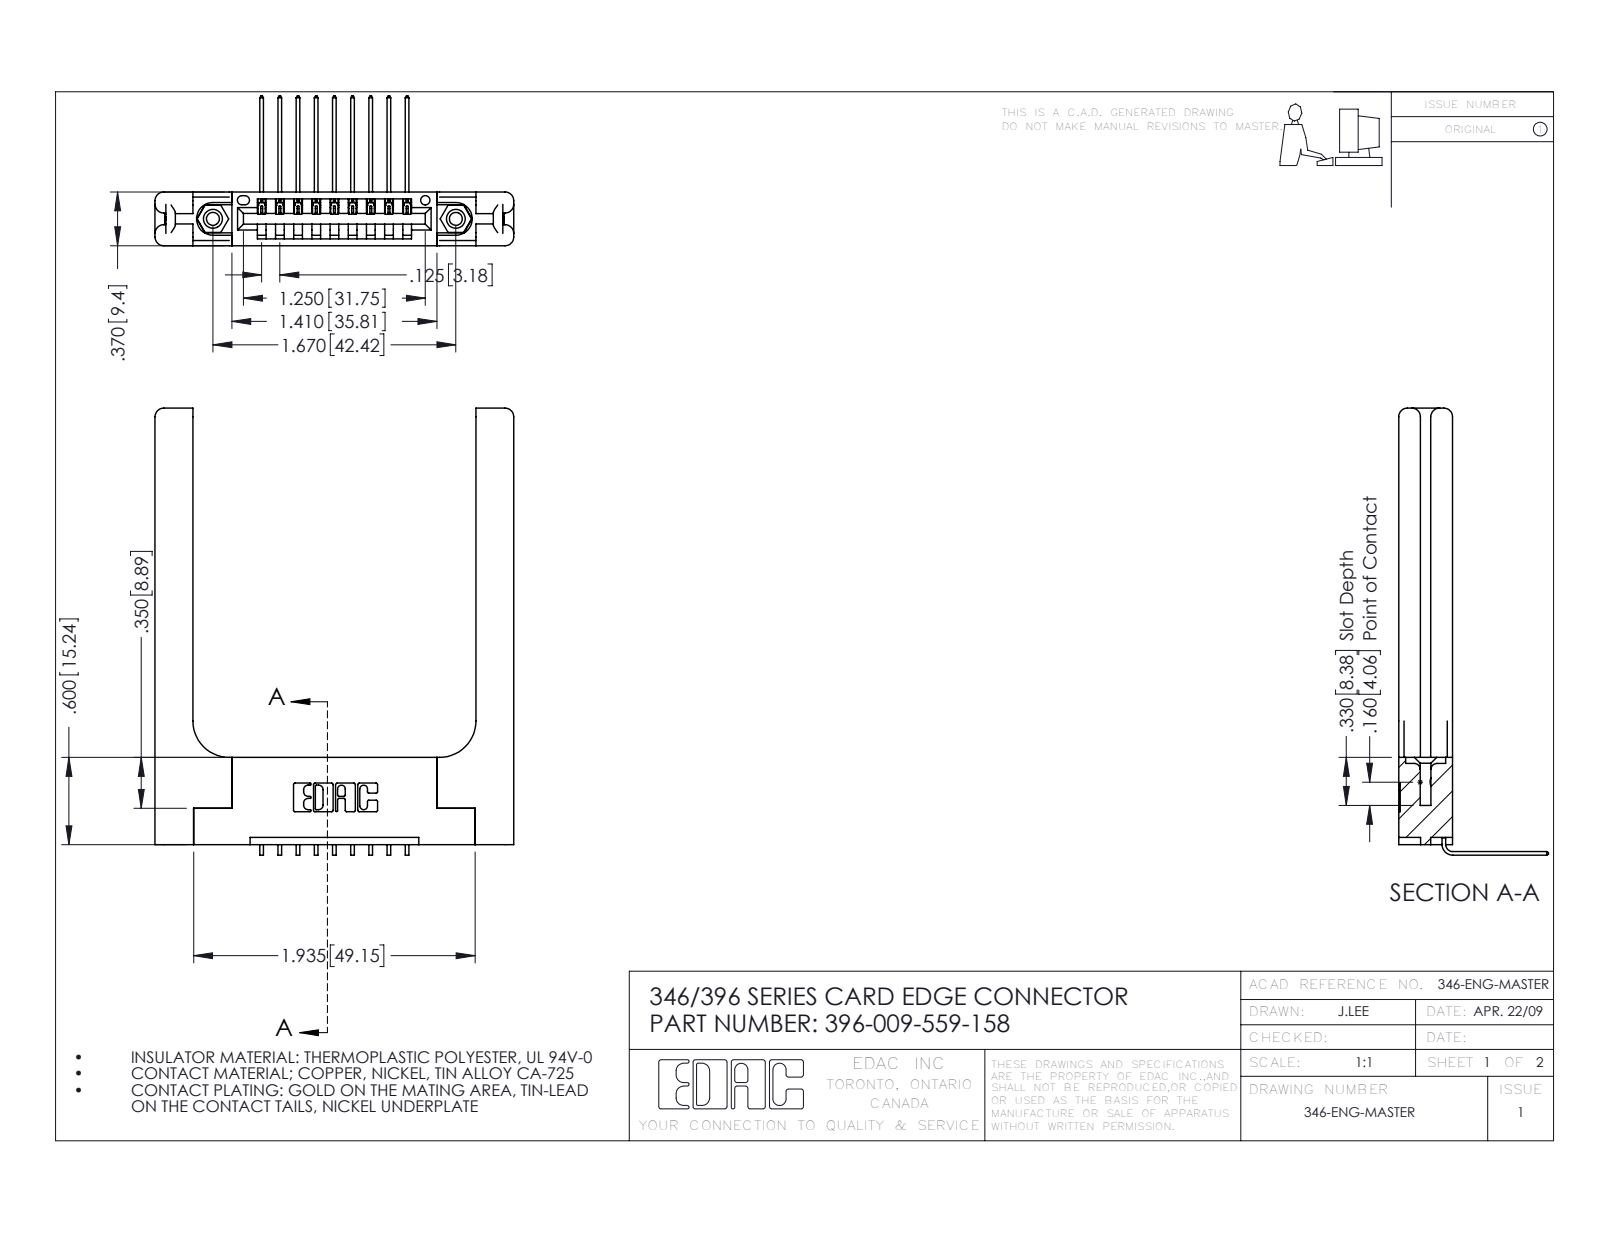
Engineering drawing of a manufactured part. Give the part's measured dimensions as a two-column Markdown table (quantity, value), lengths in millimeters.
| quantity | value |
| --- | --- |
| part name | 396-009-559-158; 346 Part_Flush Mounting Lugs - 0.156 Dia-TH; 345-292-001_558 559 Tail - 1; 346-220-058_345-220-058 (+1 more) |
| STEP written by | SolidWorks 2016 (CONFIG_CONTROL_DESIGN) |
| units | millimeters |
| bodies | 14 solids, 918 faces (602 planar, 256 cylindrical, 60 other) |
| overall size | 78.1 × 62.6 × 26.2 |
| volume | 13 300 mm³ |
| surface area | 12 240 mm² |
| round holes (diameter × count) | 2.3 × 2, 3.2 × 2, 4 × 2, 1.6 × 1 |
| round bosses / shafts (diameter × count) | 3.9 × 2 |
| partial cylindrical surfaces (radius × count) | 0.3 × 22, 0.2 × 18, 1.5 × 16, 0.2 × 6, 0.8 × 6, 0.7 × 3, 0.8 × 2, 0.8 × 2 |
| main face-to-face distances | 9.4, 3.8, 1.8, 5.6, 3.8, 8.2, 1.2, 6.4, 2.6, 4.4 |
| hole center spacings | 6.2, 37.2, 42.4 |
